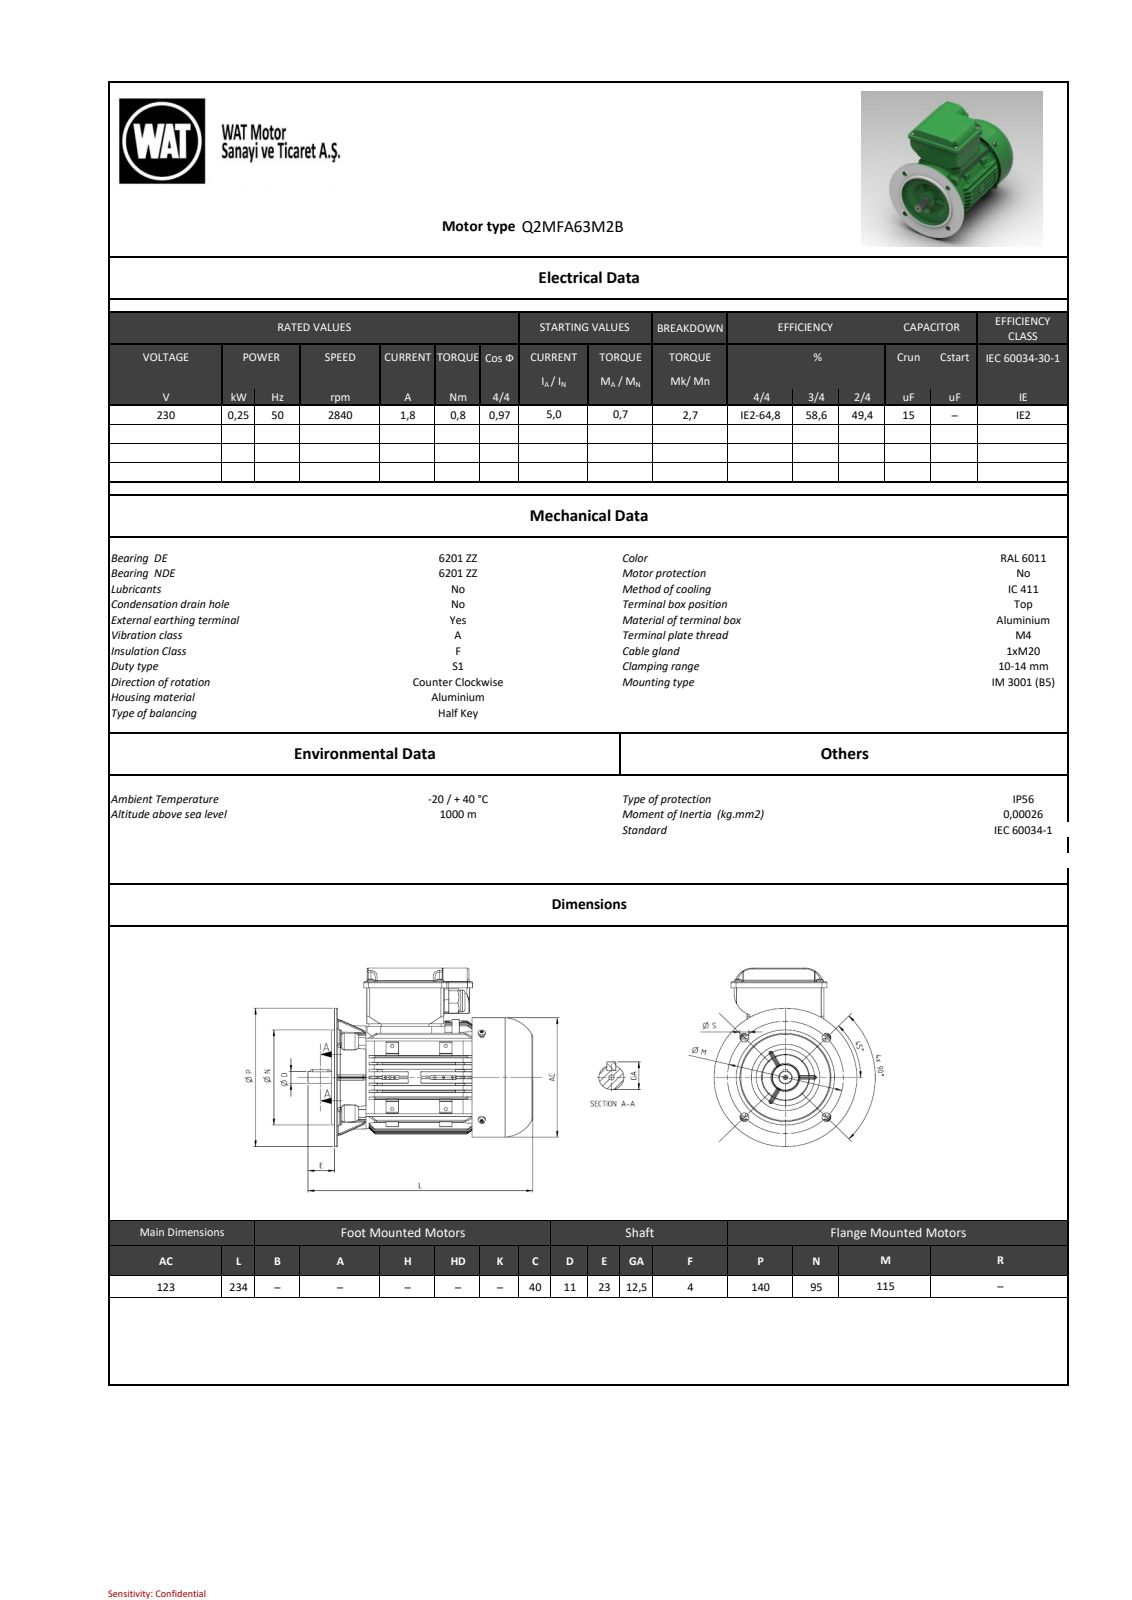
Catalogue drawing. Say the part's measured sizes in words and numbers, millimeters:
The part is named "BY6434017xx_004-TK_QM63-80; BY6424130xx_004-TKK_QM63-80; BY6434010xx_005-MOTOR_KAPAGI_QS63_FA_ISLEME; BY6423003xx_006-FAN_KAPAGI_QS63 (+6 more)". Its 3-D file was written by "SIEMENS PLM Software NX2206.8101 (AUTOMOTIVE_DESIGN)". It is 34 solids with 2175 faces: 1126 planar, 713 cylindrical and 336 other. Overall it measures 233.47 by 188.6 by 140.2 millimeters. Its volume is 636 594 cubic millimeters and its surface area 423 821 square millimeters. Round holes: 10 of diameter 3.65, 8 of diameter 4, 8 of diameter 4.5, 8 of diameter 10, 6 of diameter 2.5, 5 of diameter 3.3, 4 of diameter 4.65, 4 of diameter 4.8, 3 of diameter 3, 1 of diameter 5, 1 of diameter 8, 1 of diameter 12.2. Round bosses or shafts: 8 of diameter 8, 8 of diameter 4, 8 of diameter 3, 4 of diameter 4.8, 1 of diameter 140.2, 1 of diameter 123, 1 of diameter 95, 1 of diameter 25.28. Partial cylindrical surfaces (rounded edges, fillets, slot ends): 210 of radius 0.5, 67 of radius 1, 54 of radius 2, 27 of radius 5, 20 of radius 2.5, 9 of radius 3, 9 of radius 5.5, 8 of radius 1.5. The main face-to-face distances are 3, 1, 4.5, 7.02, 27.96, 181.52, 2.5, 3.5, 1.5, 147.5. The hole center spacings are 42.93, 79.3, 103.43, 103.58, 55, 42.98, 44.01, 57.5.
